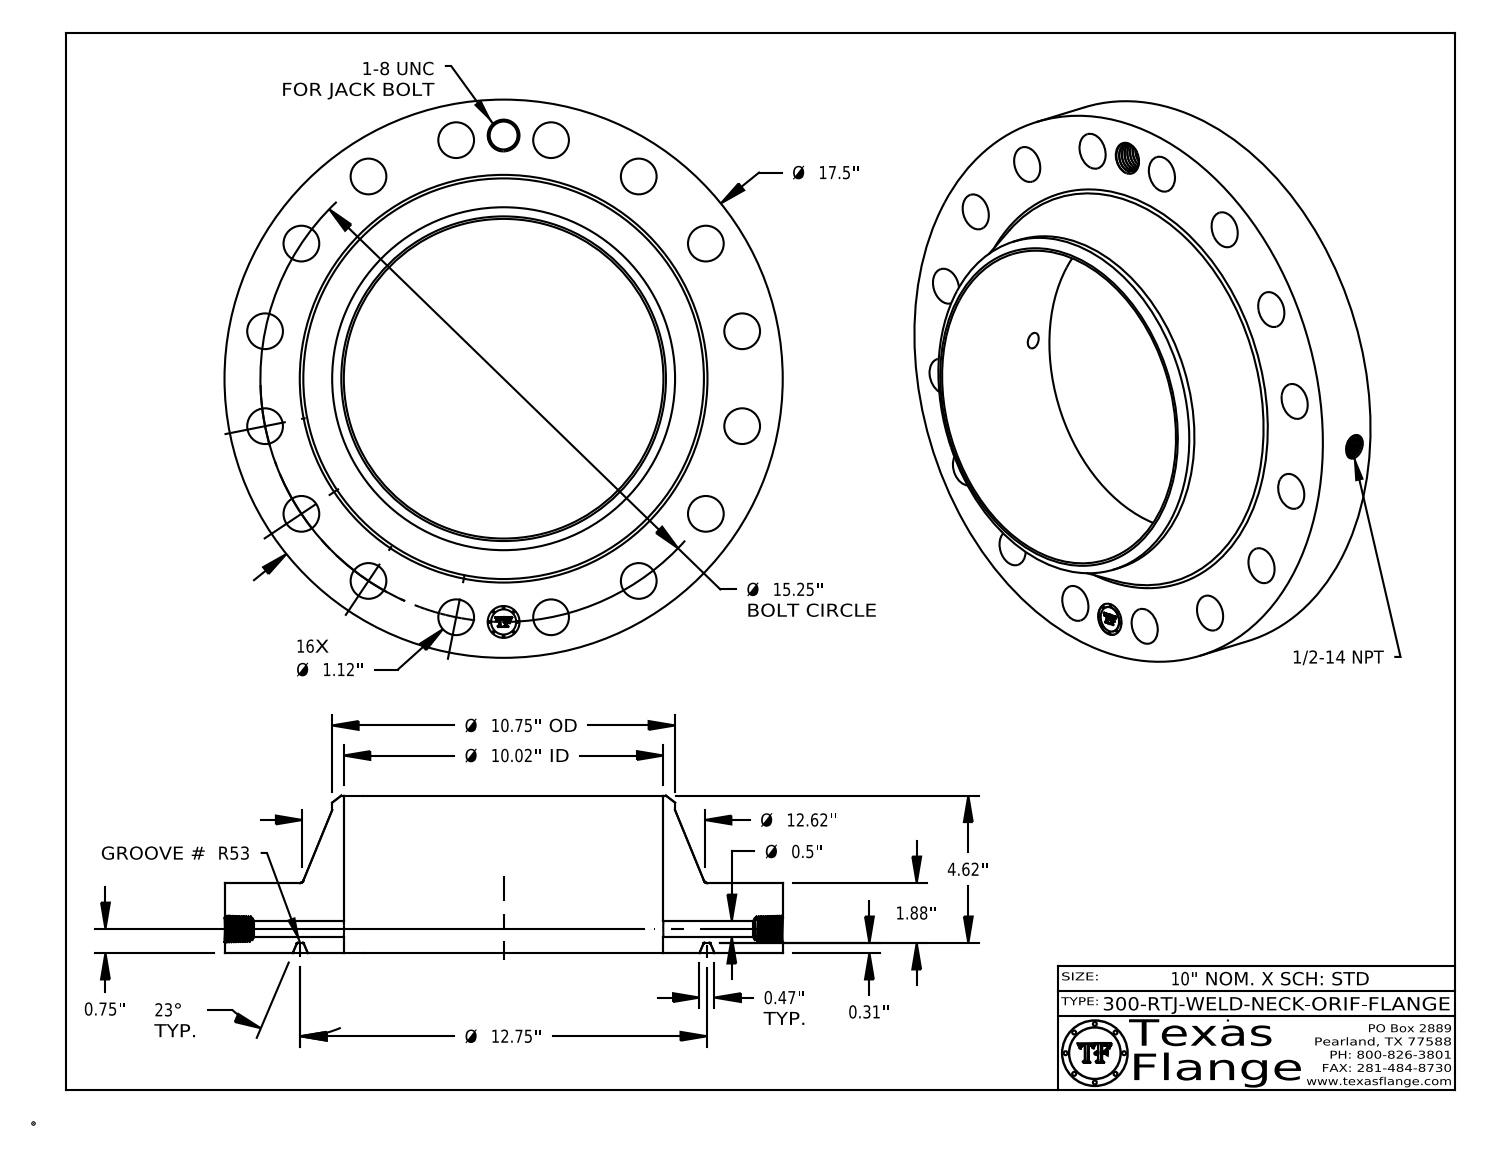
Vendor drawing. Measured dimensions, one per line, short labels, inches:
name: 300-RTJ-WELD-NECK
written by: CATIA V5 STEP AP214 (AUTOMOTIVE_DESIGN)
unit: in
bodies: 1 solid, 809 faces (370 planar, 112 cylindrical, 327 other)
size: 17.5 × 17.5 × 4.933
volume: 382.2 in³; area: 796.3 in²
holes: 16× ⌀1.12, 1× ⌀0.5, 1× ⌀0.672, 1× ⌀0.875, 1× ⌀1, 1× ⌀10.02
bosses: 8× ⌀0.061, 1× ⌀17.5, 1× ⌀10.75, 1× ⌀0.788
face distances: 2.193, 0.313, 1.88, 4.933, 4.62, 2.74, 0.015, 2.178, 1.865, 2.755
hole spacings: 5.836, 7.625, 10.783, 14.089, 14.957, 2.975, 2.975, 8.472
